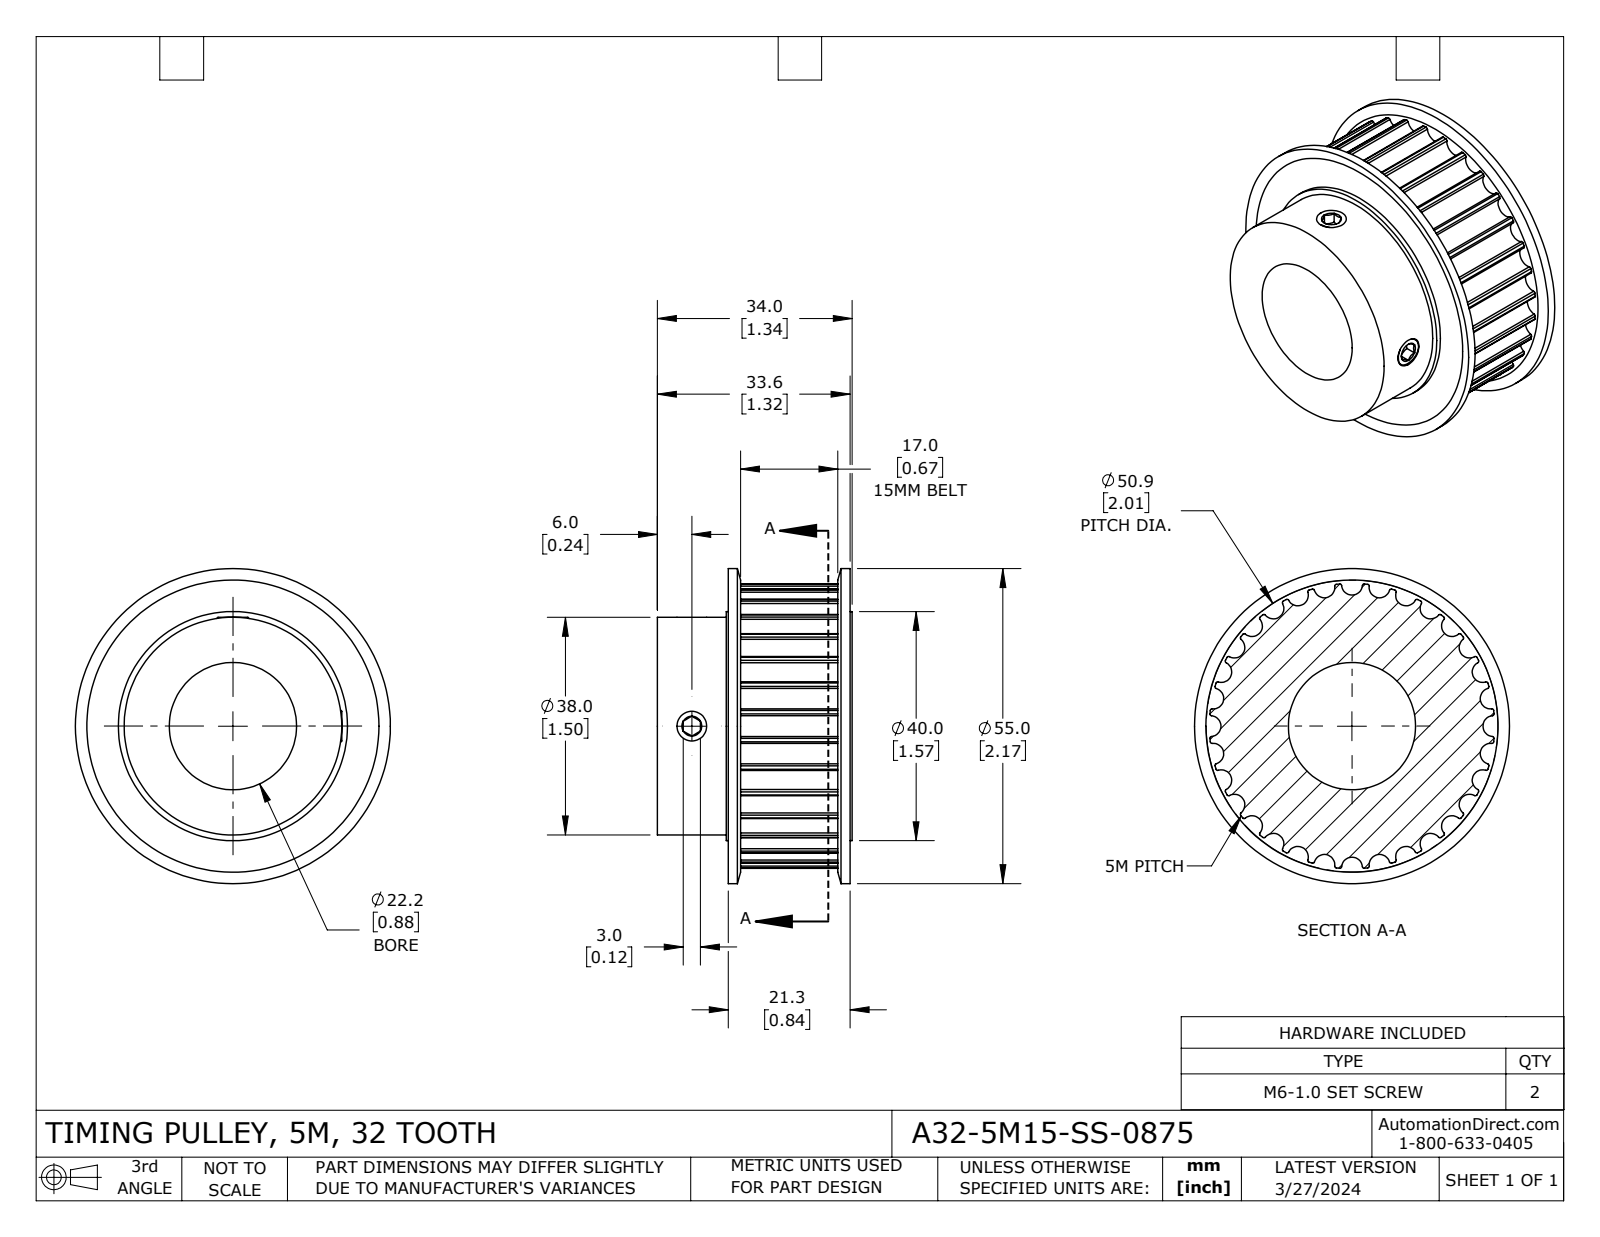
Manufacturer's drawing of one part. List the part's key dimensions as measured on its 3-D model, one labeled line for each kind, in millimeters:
Part name (STEP PRODUCT): A32-5M15-SS-0875
STEP written by: SolidWorks 2021 (CONFIG_CONTROL_DESIGN)
Units: millimetres
Bodies: 5 solids, 242 faces (25 planar, 183 cylindrical, 34 other)
Overall size (bounding box): 55 × 55 × 34
Volume: 40 095 mm³ · Surface area: 16 909 mm²
Round holes (diameter × count): ⌀5 ×2, ⌀22.23 ×1, ⌀40 ×1
Round bosses / shafts (diameter × count): ⌀6 ×2, ⌀55 ×1, ⌀38 ×1
Partial cylindrical surfaces — rounded edges, fillets, slot ends (radius × count): R0.3 ×64, R1.82 ×32, R24.89 ×1
Main face-to-face distances: 1.6, 18.6, 17, 2.5, 19.5, 0.9, 21.1, 20.2, 34, 33.1
